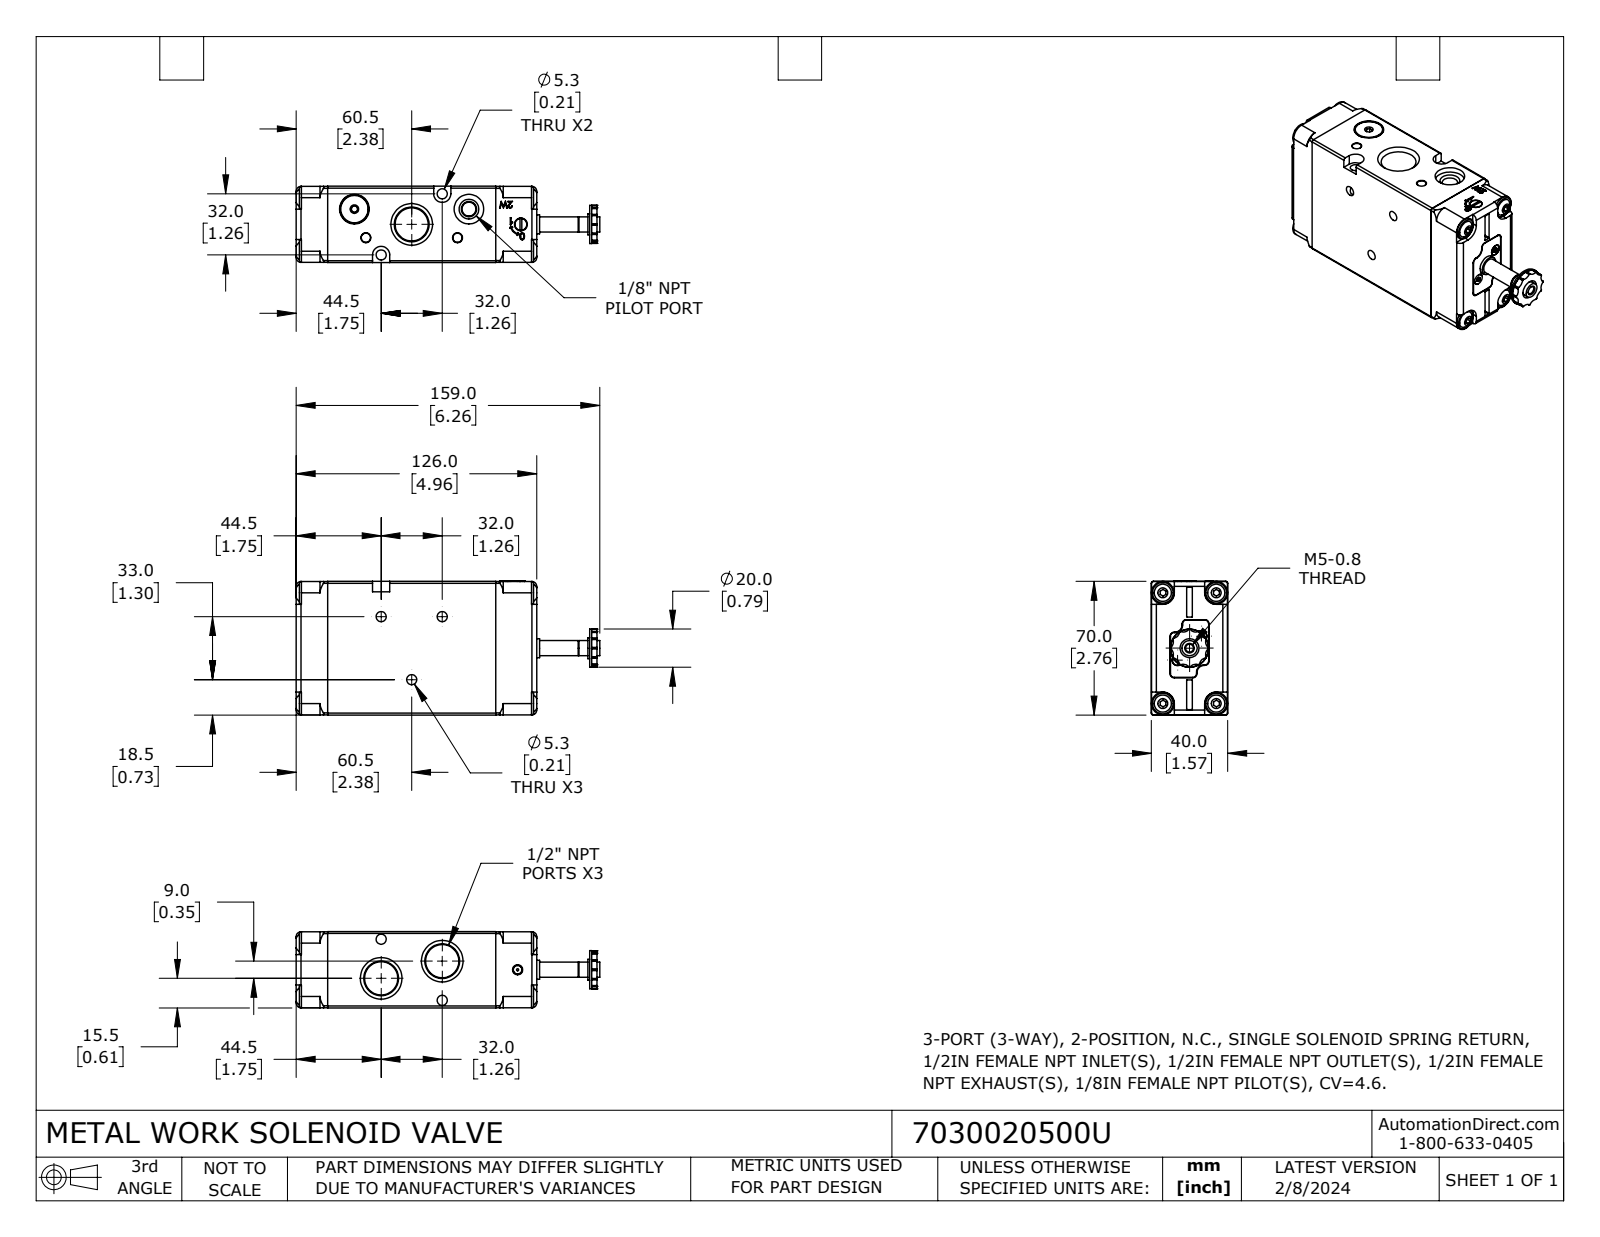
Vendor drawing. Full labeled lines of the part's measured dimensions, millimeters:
Part name (STEP PRODUCT): 7030020500U
STEP written by: SolidWorks 2023 (CONFIG_CONTROL_DESIGN)
Units: millimetres
Bodies: 3 solids, 604 faces (264 planar, 246 cylindrical, 94 other)
Overall size (bounding box): 159 × 70.2 × 40
Volume: 331 300 mm³ · Surface area: 54 540 mm²
Round holes (diameter × count): ⌀5.3 ×5, ⌀4.8 ×2, ⌀5.8 ×2, ⌀15.5 ×2, ⌀4.1 ×1, ⌀6.7 ×1, ⌀10.2 ×1, ⌀15 ×1
Round bosses / shafts (diameter × count): ⌀5.5 ×2, ⌀20 ×1, ⌀19.9 ×1, ⌀15 ×1, ⌀11 ×1, ⌀10 ×1, ⌀8 ×1, ⌀7.6 ×1
Partial cylindrical surfaces — rounded edges, fillets, slot ends (radius × count): R0.2 ×12, R0.3 ×12, R0.5 ×12, R3.8 ×12, R0.3 ×8, R1 ×8, R2.5 ×8, R2 ×6
Main face-to-face distances: 40, 88, 39.9, 70, 21.5, 39.8, 69.9, 16.5, 104.5, 126
Hole centre spacings: 8.8, 16.2, 36.7, 56, 12, 16.1, 17.7, 24.4
